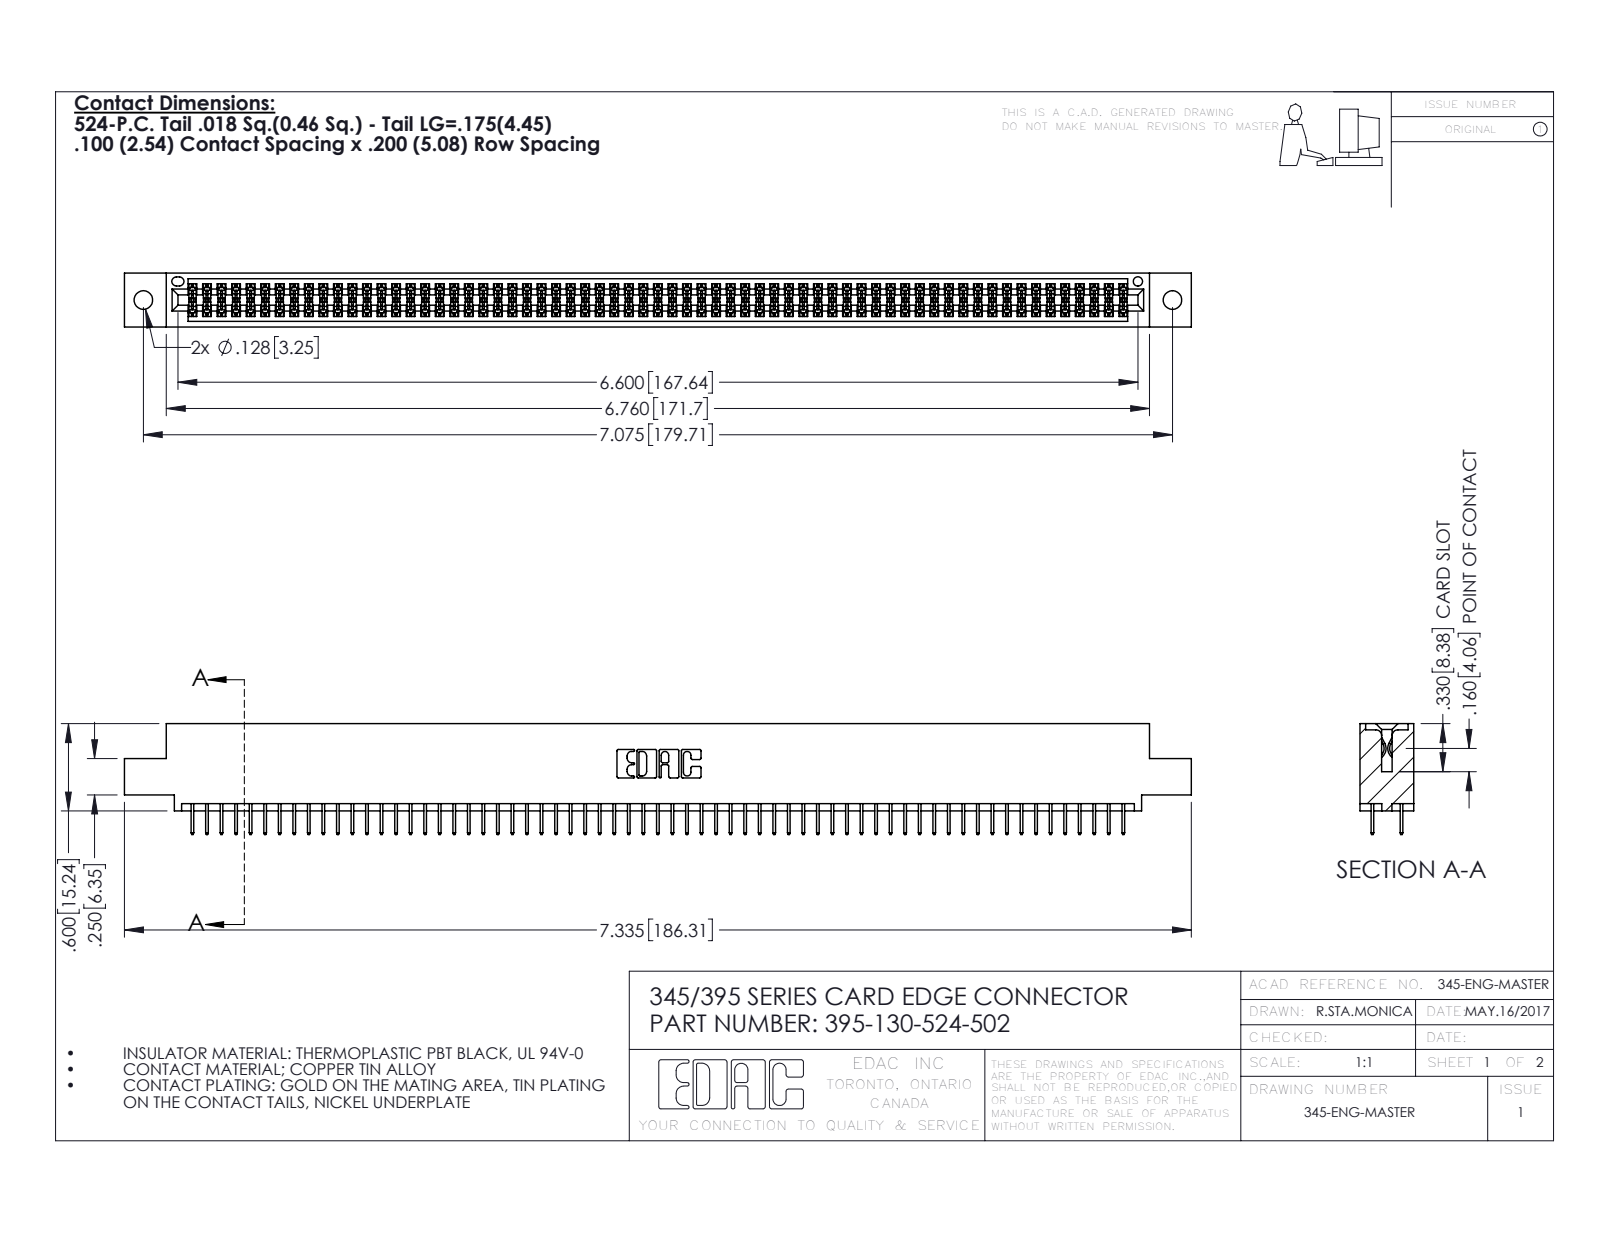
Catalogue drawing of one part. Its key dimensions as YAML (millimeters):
part_name: "395-130-524-502; 345-292-001_345-293-124; 345 Part_0.110 Offset - 0.128 Dia"
step_written_by: "SolidWorks 2016 (CONFIG_CONTROL_DESIGN)"
units: millimeters
bodies: {solids: 131, faces: 7150, planar: 5154, cylindrical: 1996, other: 0}
overall_size: [186.3, 19.4, 9.4]
volume: 18010
surface_area: 26360
round_holes:
  - {diameter: 3.3, count: 2}
  - {diameter: 1.6, count: 1}
partial_cylinders:
  - {radius: 0.2, count: 195}
  - {radius: 0.3, count: 22}
  - {radius: 0.2, count: 6}
  - {radius: 0.8, count: 6}
  - {radius: 0.7, count: 3}
  - {radius: 0.4, count: 2}
  - {radius: 0.5, count: 2}
  - {radius: 0.6, count: 2}
face_to_face_distances: [1.8, 7.6, 5.1, 9.4, 2.5, 6.9, 0.6, 5.7, 1.8, 4.4]
hole_center_spacings: [6.9, 173.7, 179.7]
